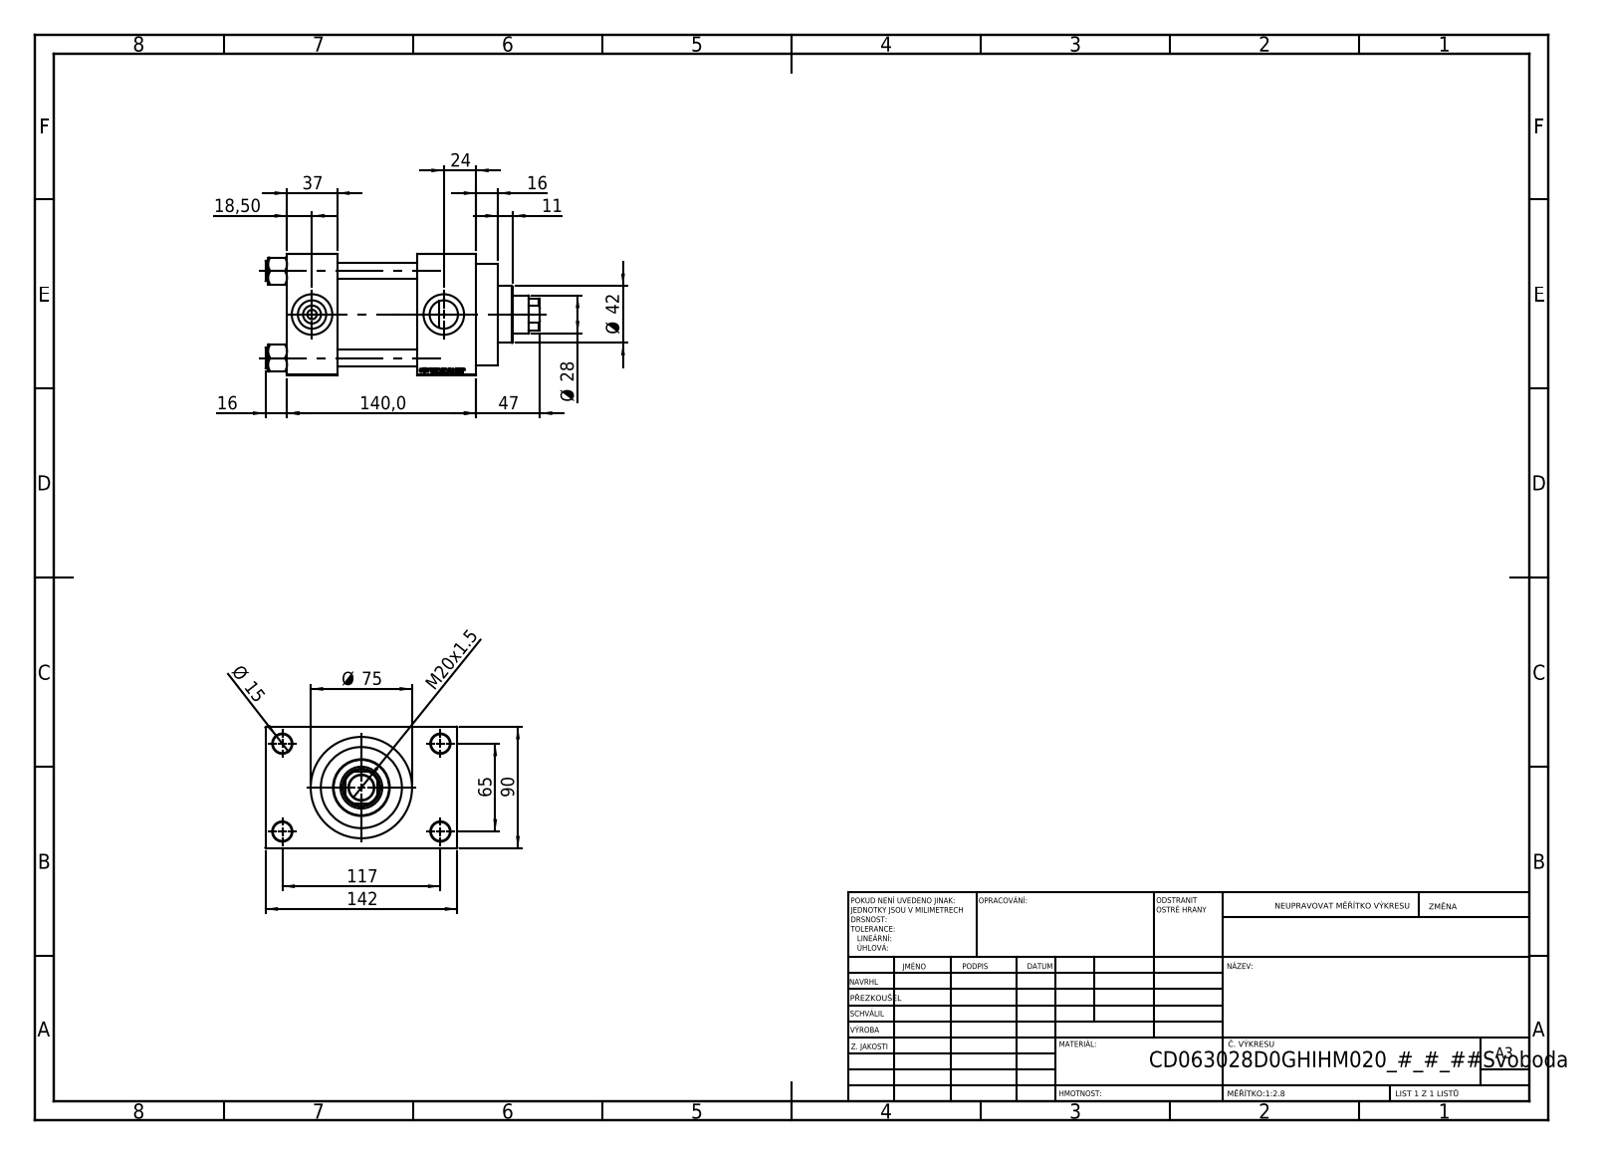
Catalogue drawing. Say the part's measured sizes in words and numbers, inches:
The part is named "V215CD_VC_A; V215CD_D_Body; V215CD_NUT_M5_D; V215CD_VCP_D (+1 more)". Its 3-D file was written by "SolidWorks 2019 (CONFIG_CONTROL_DESIGN)". It is 11 solids with 1103 faces: 497 planar, 88 cylindrical and 518 other. Overall it measures 7.992 by 5.591 by 3.543 inches. Its volume is 66.88 cubic inches and its surface area 310.5 square inches. Round holes: 4 of diameter 0.472, 4 of diameter 0.551, 2 of diameter 0.276, 2 of diameter 0.825, 2 of diameter 1.181, 1 of diameter 0.728, 1 of diameter 1.102, 1 of diameter 1.22, 1 of diameter 1.969, 1 of diameter 2.362, 1 of diameter 2.48. Round bosses or shafts: 4 of diameter 0.591, 1 of diameter 2.953, 1 of diameter 2.717, 1 of diameter 1.654. Partial cylindrical surfaces (rounded edges, fillets, slot ends): 1 of radius 0.531. The main face-to-face distances are 3.543, 2.323, 1.457, 3.78, 5.512, 4.055, 1.732, 1.024, 4.567, 0.63. The hole center spacings are 1.037, 1.79, 2.531, 2.635, 2.748, 3.569, 4.383, 2.559.
